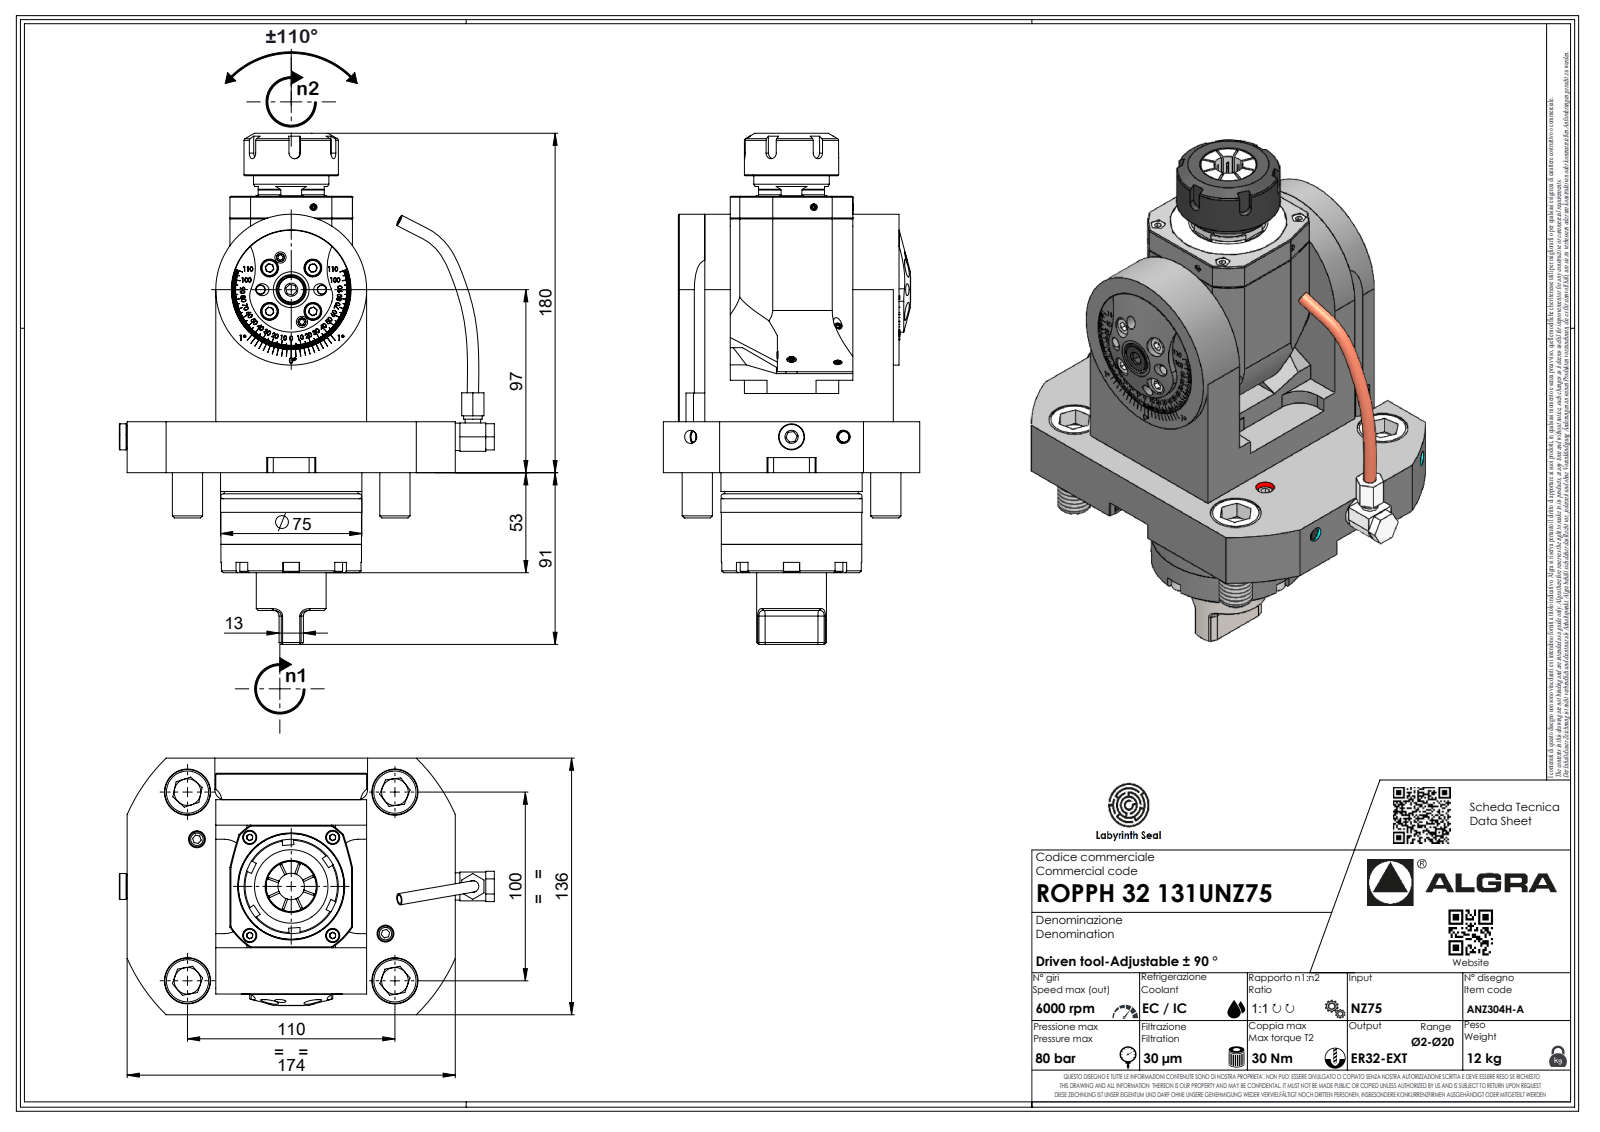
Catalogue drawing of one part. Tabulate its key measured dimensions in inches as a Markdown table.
| quantity | value |
| --- | --- |
| part name | ROPPH32131UNZ75 |
| STEP written by | SolidWorks 2023 (AUTOMOTIVE_DESIGN) |
| units | inches |
| bodies | 1 solid, 625 faces (394 planar, 106 cylindrical, 125 other) |
| overall size | 10.666 × 7.665 × 5.354 |
| volume | 107.1 in³ |
| surface area | 235.3 in² |
| round holes (diameter × count) | 0.083 × 1 |
| round bosses / shafts (diameter × count) | 3.15 × 1, 2.949 × 1, 2.933 × 1, 2.791 × 1, 1.969 × 1, 1.575 × 1, 1.457 × 1, 0.571 × 1 |
| partial cylindrical surfaces (radius × count) | 0.118 × 11, 0.276 × 8, 0.315 × 8, 0.013 × 7, 0.02 × 7, 0.146 × 7, 0.472 × 4, 0.157 × 2 |
| main face-to-face distances | 1.063, 3.15, 0.315, 2.559, 4.705, 3.957, 1.398, 1.85, 0.748, 2.854 |
